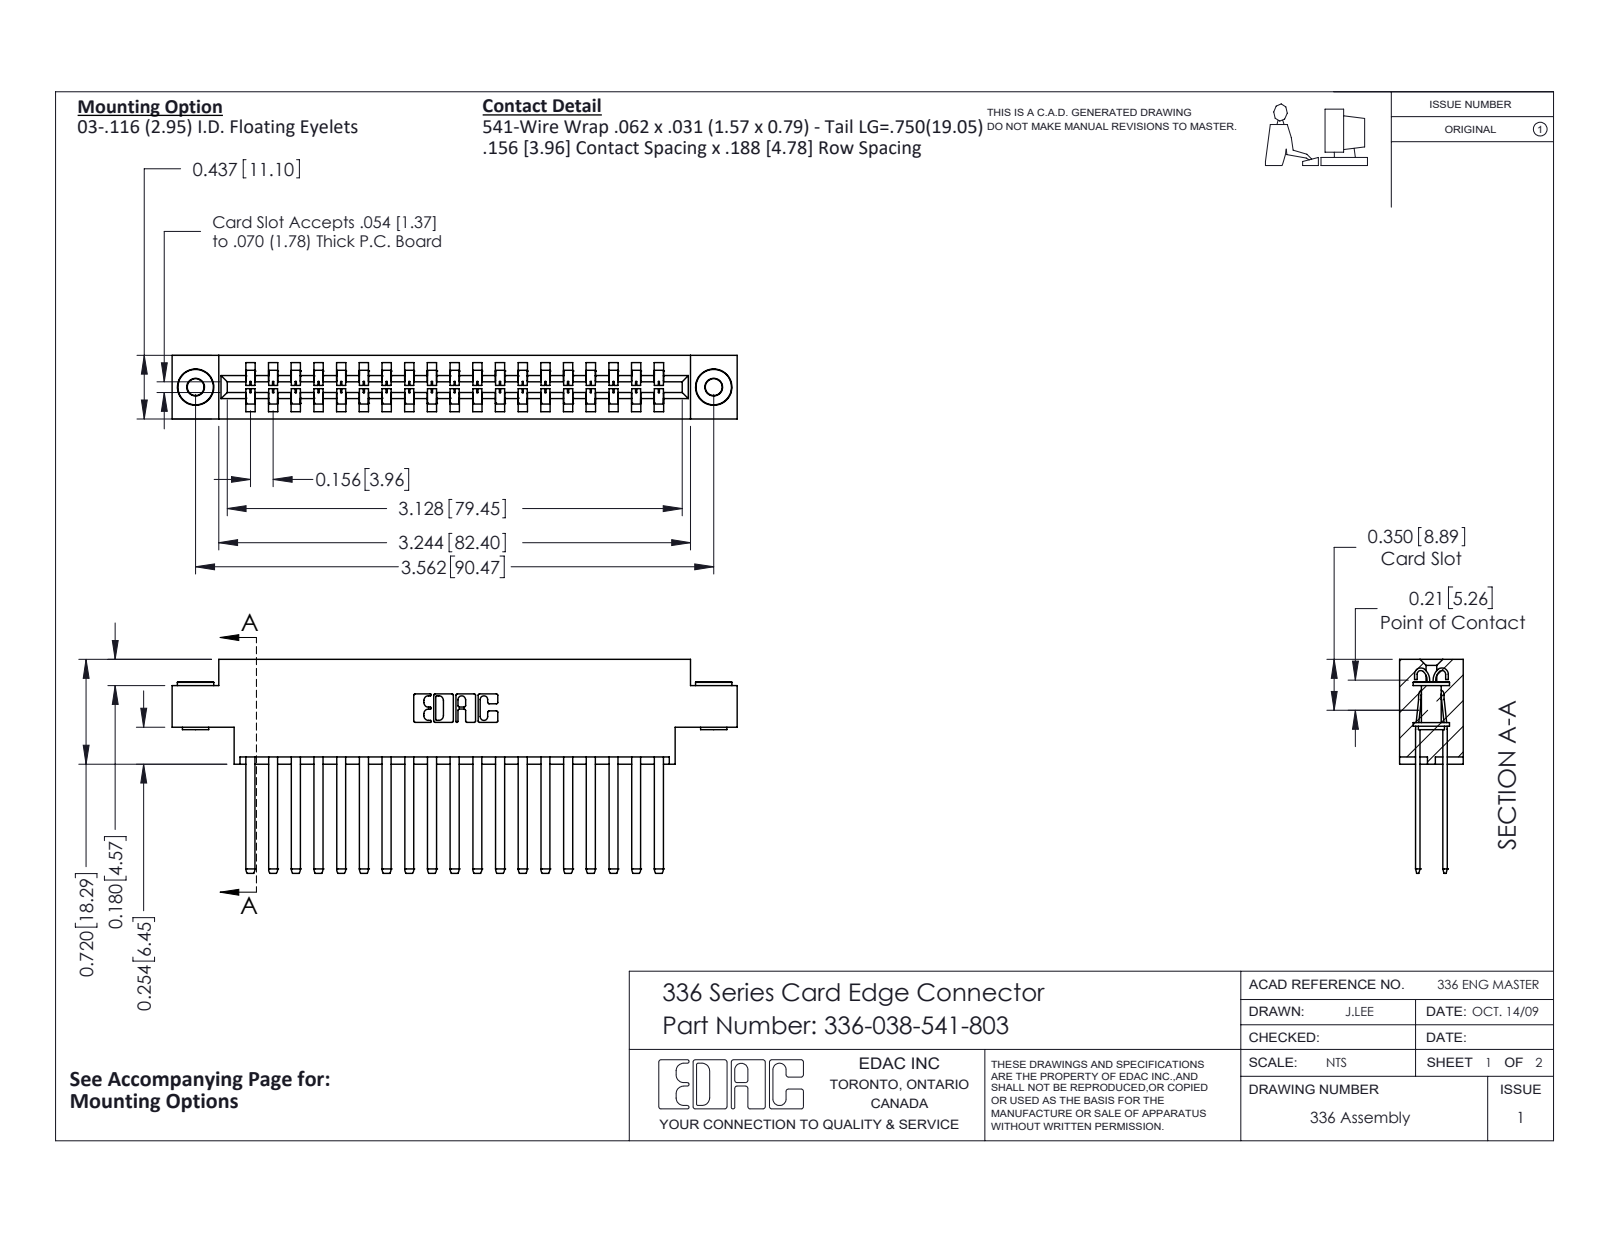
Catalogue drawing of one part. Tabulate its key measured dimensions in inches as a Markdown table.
| quantity | value |
| --- | --- |
| part name | 336-290-001_336-290-541; 345-250-002_345-250-002-102; 336-038-541-803; 336 Part_Offset - .156 Dia - TH |
| STEP written by | SolidWorks 2020 (CONFIG_CONTROL_DESIGN) |
| units | inches |
| bodies | 41 solids, 1752 faces (1072 planar, 672 cylindrical, 8 other) |
| overall size | 3.885 × 1.47 × 0.437 |
| volume | 0.885 in³ |
| surface area | 28.47 in² |
| round holes (diameter × count) | 0.116 × 2, 0.156 × 2 |
| round bosses / shafts (diameter × count) | 0.25 × 2, 0.18 × 2, 0.136 × 2 |
| partial cylindrical surfaces (radius × count) | 0.004 × 76, 0.056 × 38, 0.01 × 22, 0.007 × 6, 0.031 × 6, 0.022 × 4, 0.04 × 4, 0.026 × 3 |
| main face-to-face distances | 0.188, 0.031, 0.328, 0.14, 0.297, 0.109, 0.437, 0.033, 0.181, 0.256 |
| hole center spacings | 3.562 |
